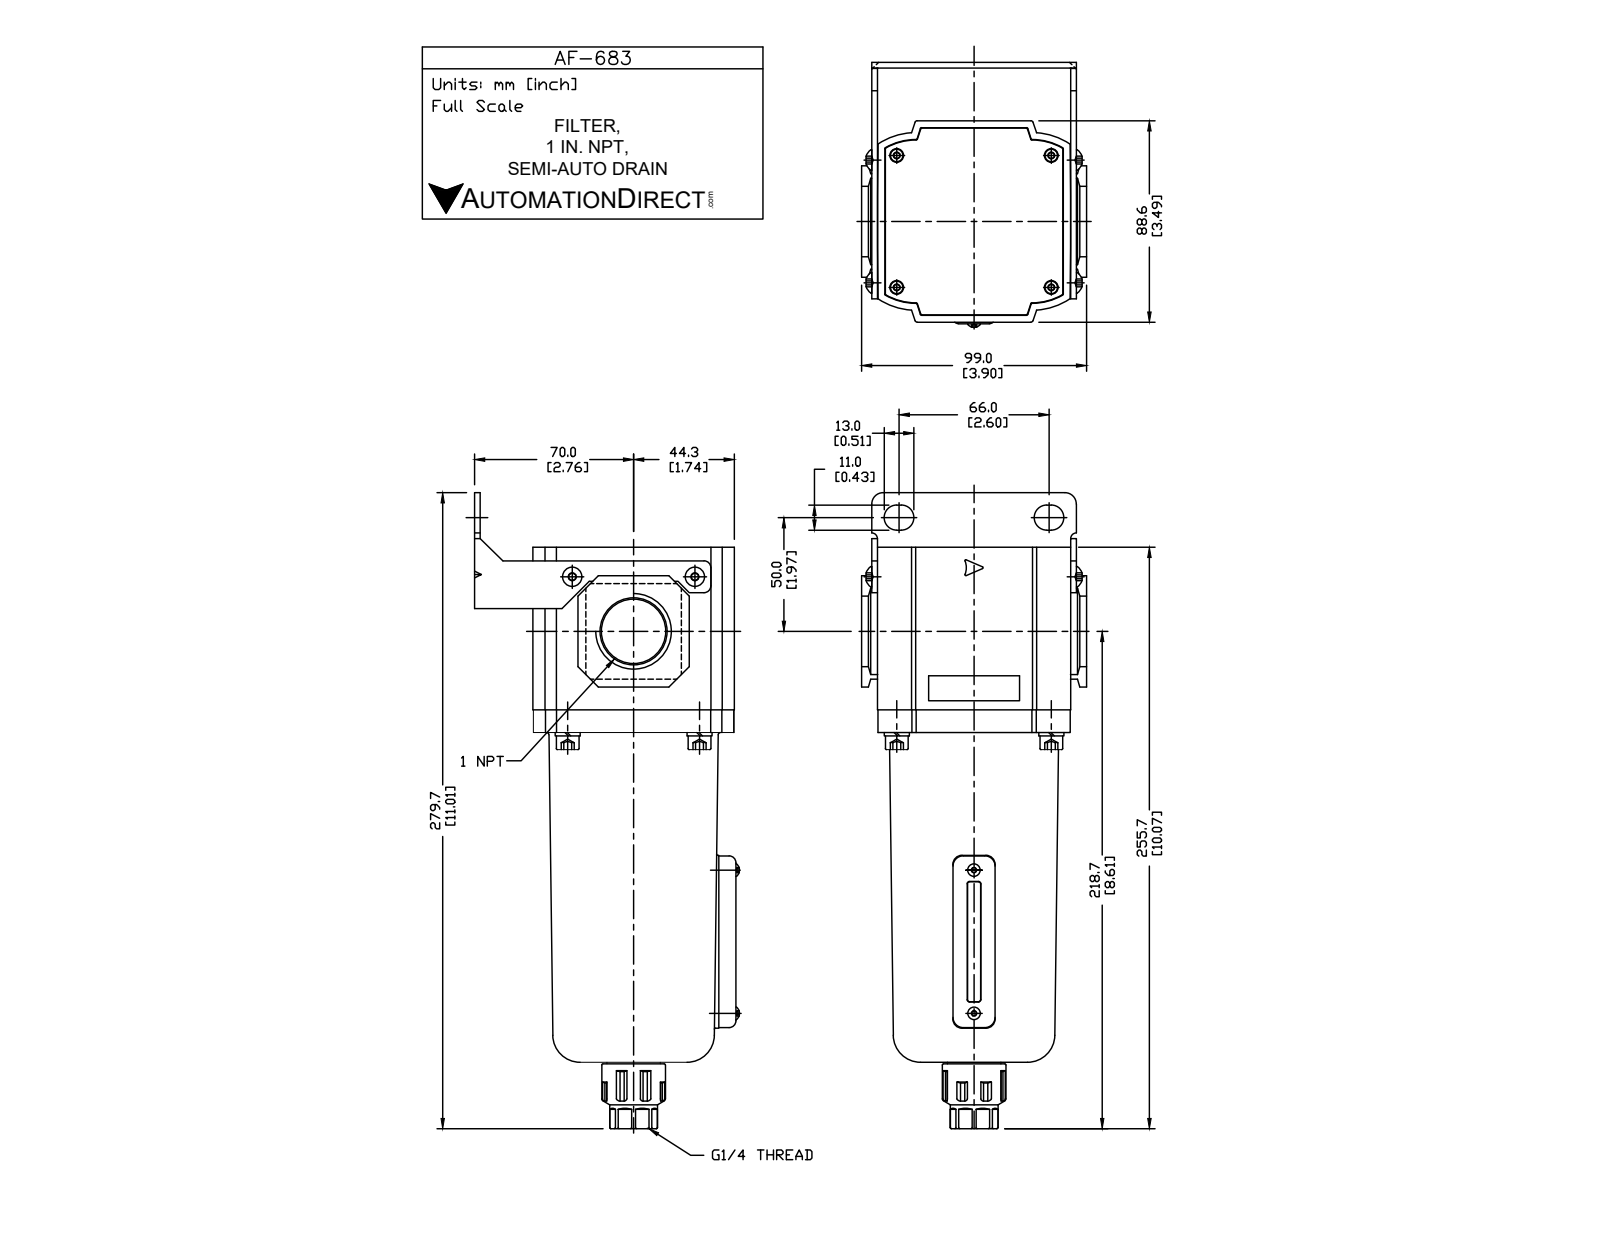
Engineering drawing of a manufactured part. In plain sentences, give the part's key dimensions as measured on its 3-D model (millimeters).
The part is named "AF-683". Its 3-D file was written by "SolidWorks 2015 (CONFIG_CONTROL_DESIGN)". It is 8 solids with 384 faces: 233 planar, 88 cylindrical and 63 other. Overall it measures 280 by 116.49 by 99 millimeters. Its volume is 1 224 000 cubic millimeters and its surface area 120 794 square millimeters. Round holes: 2 of diameter 5.5, 1 of diameter 11.45, 1 of diameter 28.98. Round bosses or shafts: 4 of diameter 10, 1 of diameter 74.5, 1 of diameter 28, 1 of diameter 21. Partial cylindrical surfaces (rounded edges, fillets, slot ends): 10 of radius 3, 8 of radius 9.5, 6 of radius 0.5, 5 of radius 2, 4 of radius 0.3, 4 of radius 1, 4 of radius 5.5, 4 of radius 29.7. The main face-to-face distances are 2.5, 71.5, 85, 25.7, 23.2, 114.3, 111.8, 88.6, 87.5, 92. The hole center spacings are 36.12, 54.
